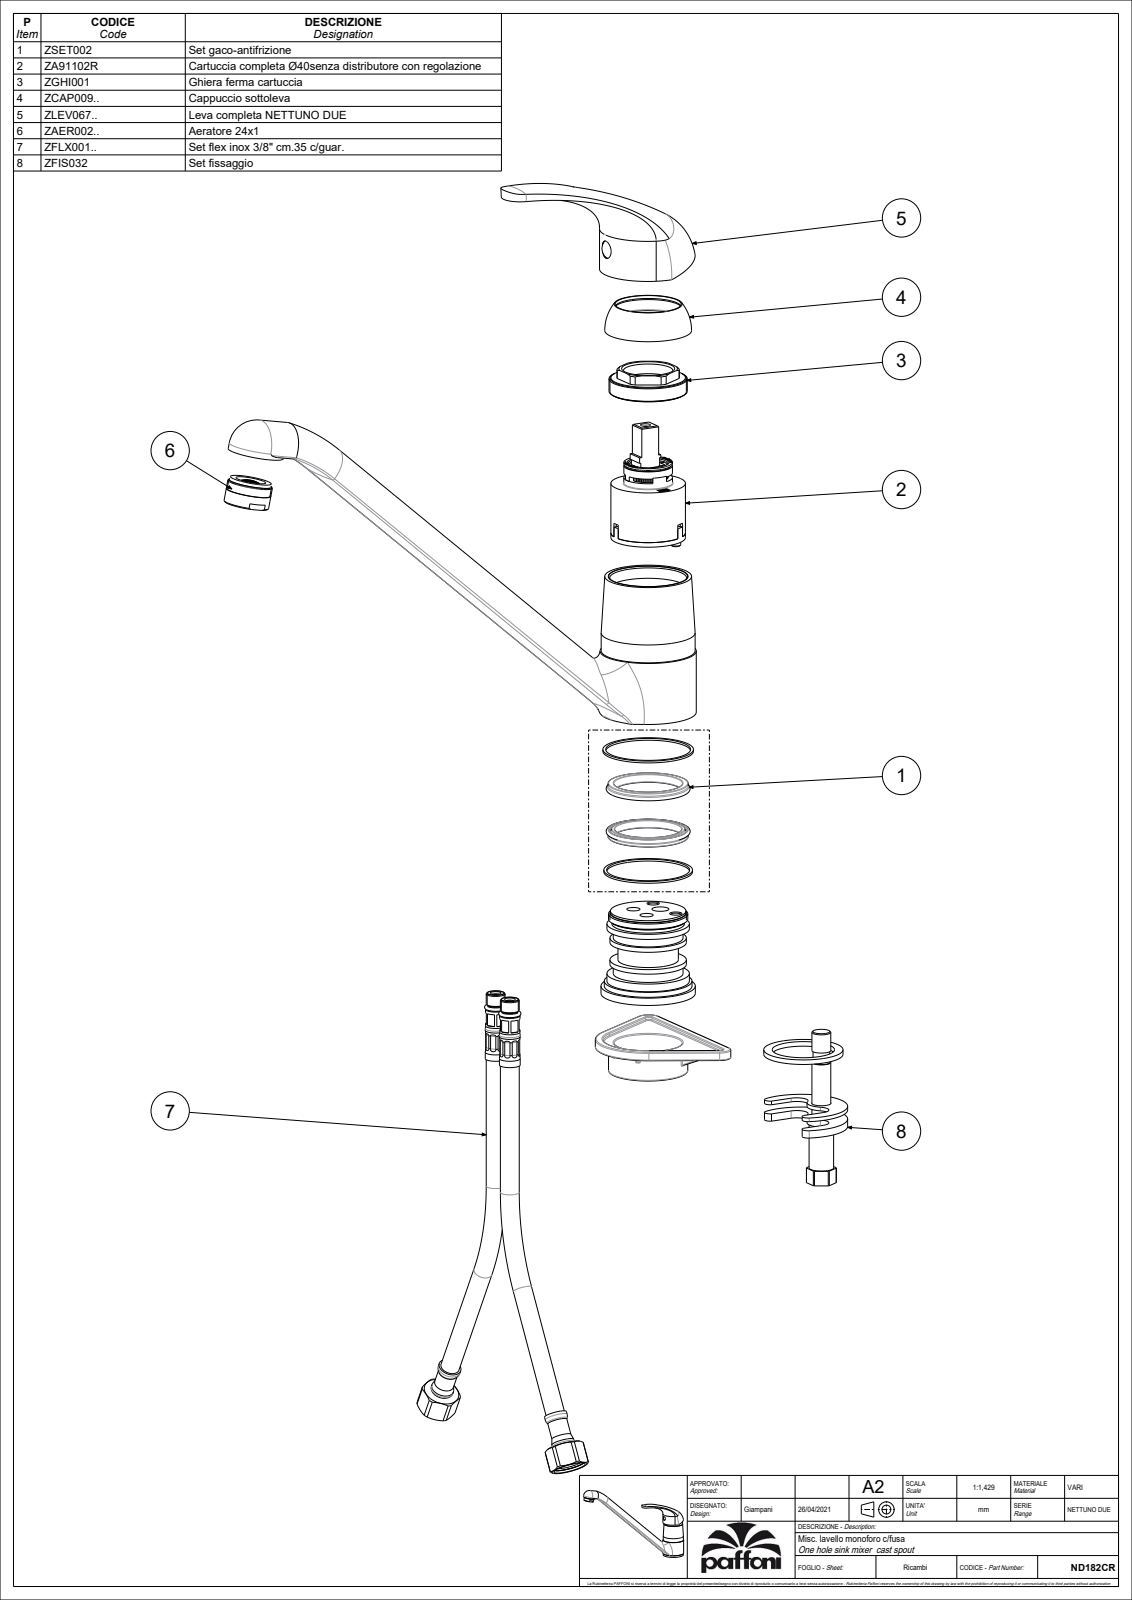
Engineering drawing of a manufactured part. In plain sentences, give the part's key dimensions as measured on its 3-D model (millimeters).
The part is named "ND182CR". Its 3-D file was written by "CREO PARAMETRIC BY PTC INC, 2020044 (CONFIG_CONTROL_DESIGN)". It is 1 solid with 118 faces: 39 planar, 30 cylindrical and 49 other. Overall it measures 280.18 by 196.38 by 51 millimeters. Its volume is 336 144 cubic millimeters and its surface area 56 856 square millimeters. Round holes: 1 of diameter 6, 1 of diameter 48.2. Round bosses or shafts: 1 of diameter 51, 1 of diameter 50, 1 of diameter 49.8, 1 of diameter 46.5, 1 of diameter 44.8, 1 of diameter 29.69, 1 of diameter 24, 1 of diameter 5. Partial cylindrical surfaces (rounded edges, fillets, slot ends): 2 of radius 14.84, 2 of radius 217.81, 1 of radius 3.9, 1 of radius 4. The main face-to-face distances are 93.4, 37.9, 55.5, 4.4, 33.5, 89, 4, 0.4, 33.9, 89.4.
